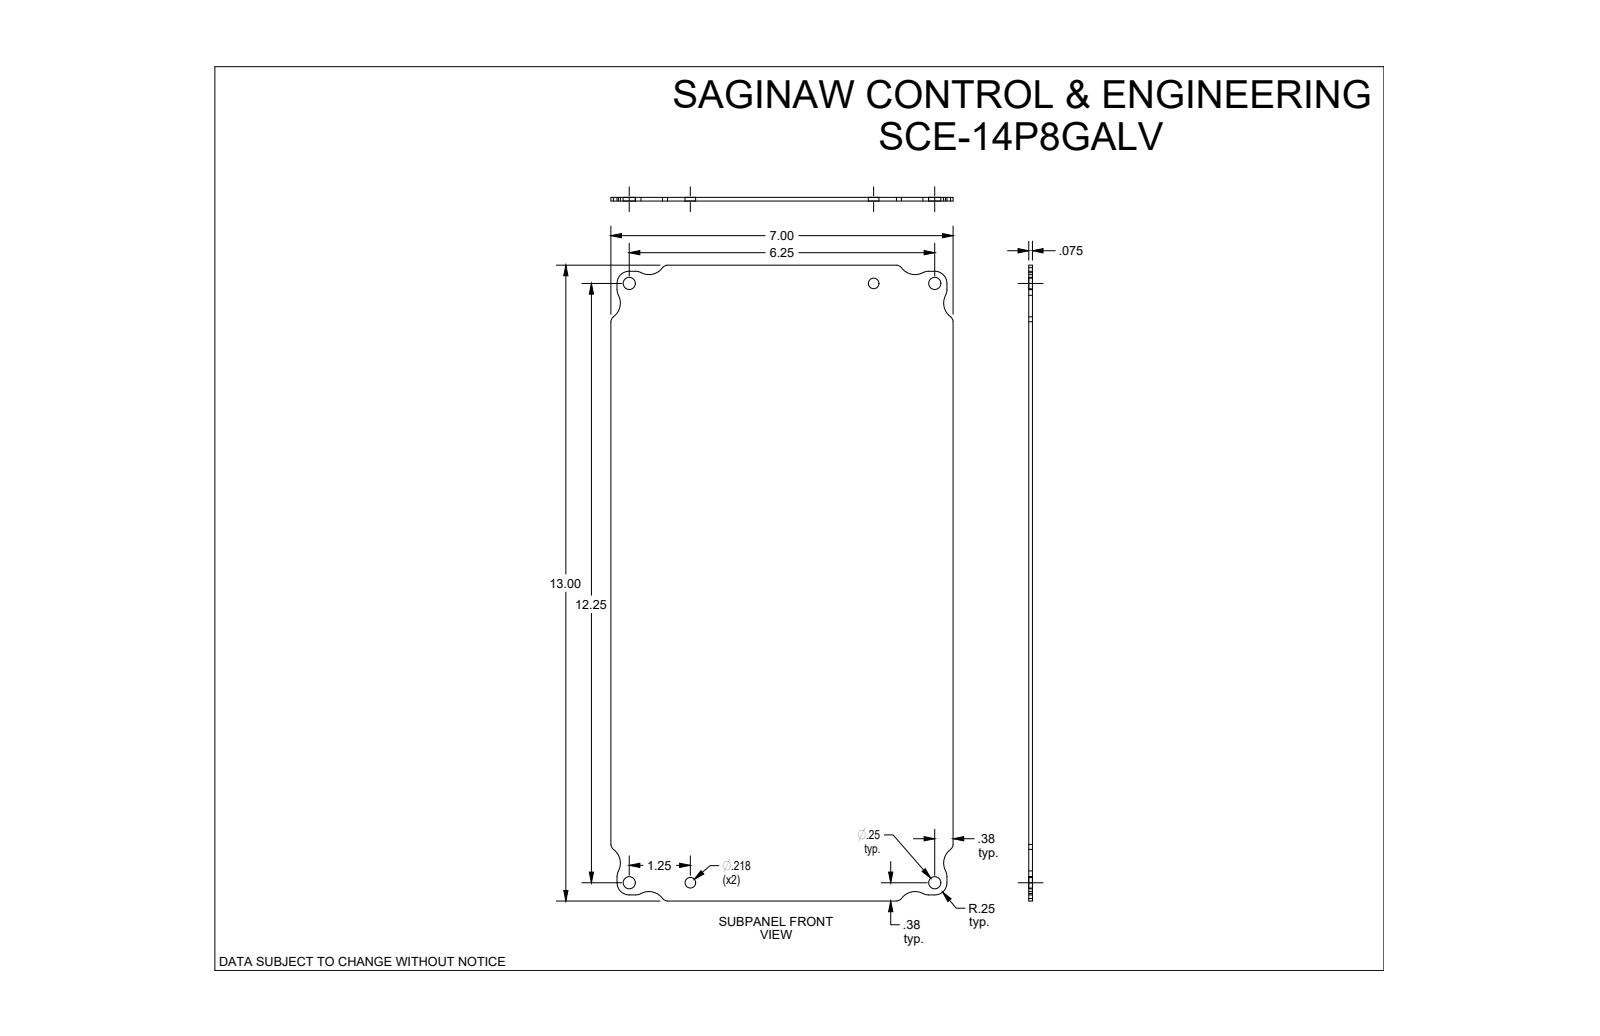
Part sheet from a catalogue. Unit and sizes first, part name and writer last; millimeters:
Units: millimetres
Overall size (bounding box): 330.2 × 177.8 × 1.9
Round holes (diameter × count): ⌀6.4 ×4, ⌀5.5 ×2
Partial cylindrical surfaces — rounded edges, fillets, slot ends (radius × count): R6.4 ×12, R3.2 ×8, R8.7 ×8
Main face-to-face distances: 1.9, 177.8, 330.2, 3.2, 327, 174.6, 323.9, 171.5
Hole centre spacings: 31.8, 127, 158.8, 311.2, 312.8, 336.1, 349.3, 325.4
Volume: 110 000 mm³ · Surface area: 117 600 mm²
Bodies: 1 solid, 48 faces (14 planar, 34 cylindrical, 0 other)
Part name (STEP PRODUCT): SCE-14P8GALV
STEP written by: SolidWorks 2019 (CONFIG_CONTROL_DESIGN)
